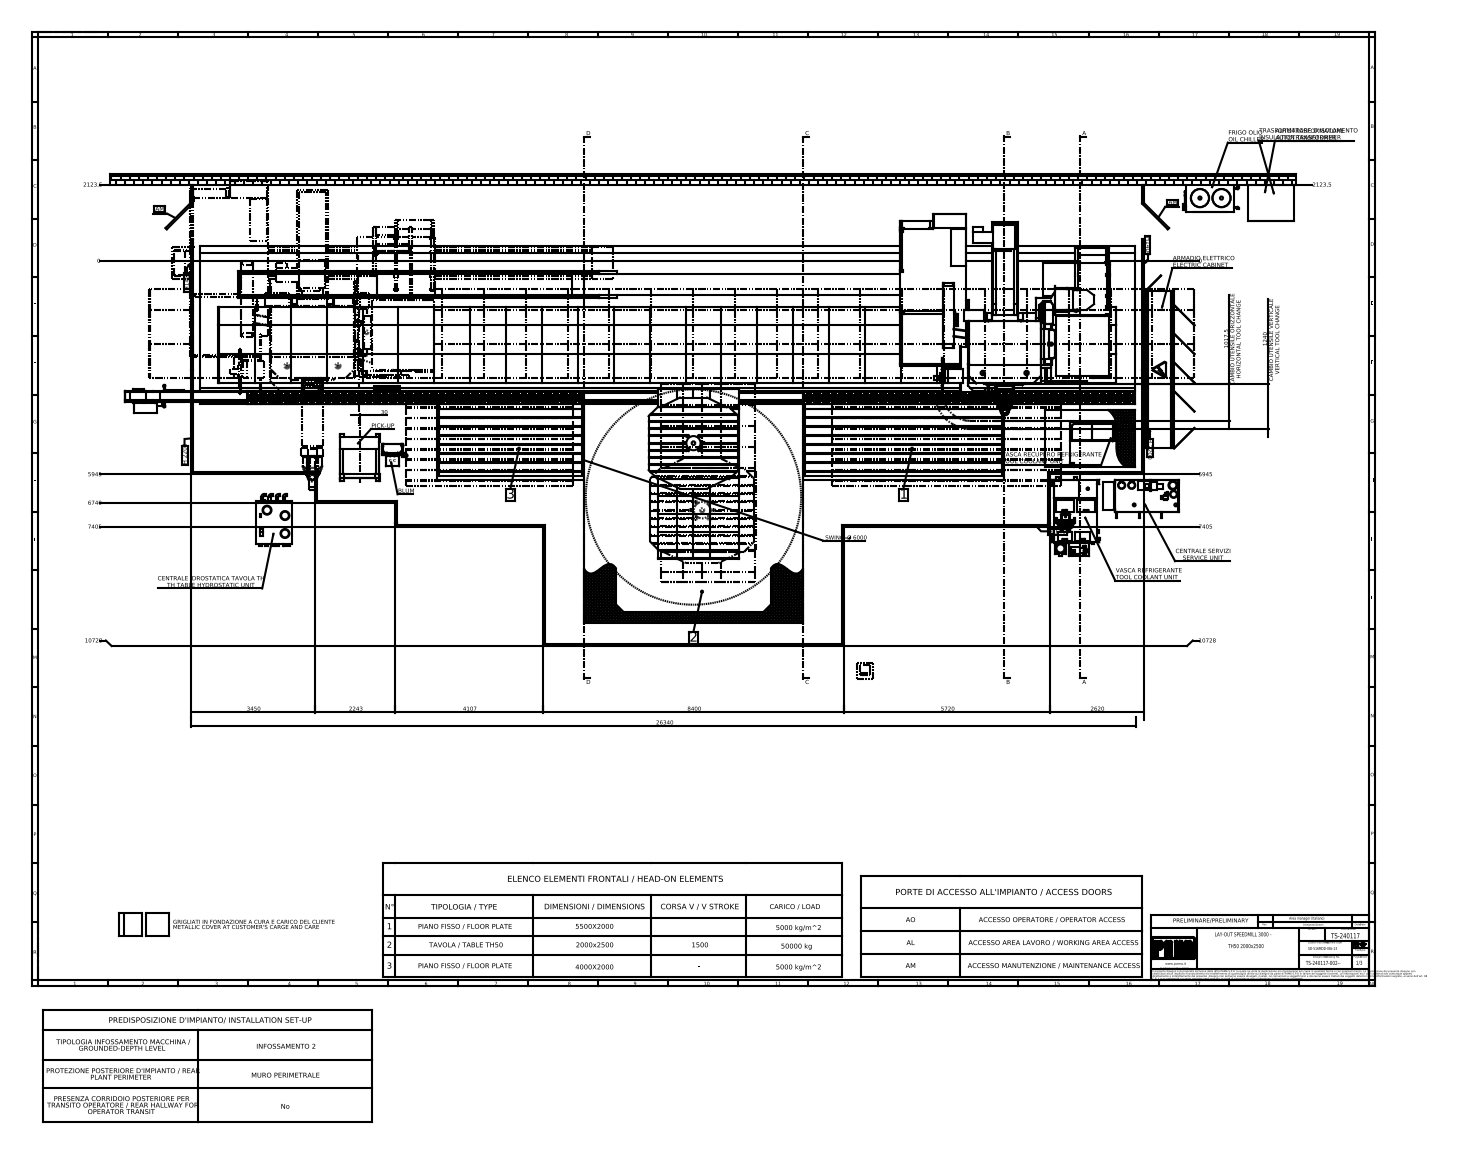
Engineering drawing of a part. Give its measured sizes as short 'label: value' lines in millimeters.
name: S001725_DRW6 (A = 0°); S003495_Y=3500; S003505_TM 5 RUOTE ISO 50; S001769 (+8 more)
written by: SolidWorks 2023 (AUTOMOTIVE_DESIGN)
unit: mm
bodies: 502 solids, 8552 faces (5762 planar, 2034 cylindrical, 756 other)
size: 33040 × 16101.5 × 9400
volume: 1 058 000 000 000 mm³; area: 3 192 000 000 mm²
holes: 196× ⌀35, 123× ⌀69.6, 17× ⌀5, 9× ⌀7, 7× ⌀11, 6× ⌀8, 6× ⌀32, 6× ⌀340, 4× ⌀6.6, 4× ⌀14, 4× ⌀21, 4× ⌀25
bosses: 14× ⌀60, 9× ⌀200, 9× ⌀80, 8× ⌀55, 8× ⌀30, 6× ⌀150, 6× ⌀35, 5× ⌀120
rounds: 225× R5, 69× R15, 60× R35, 39× R6, 33× R10, 29× R20, 21× R2, 14× R3
face distances: 2000, 300, 1340, 660, 50, 16101.5, 15801.5, 6418.5, 6118.5, 9683
hole spacings: 250, 500, 750, 1000, 1250, 1500, 1750, 2000
